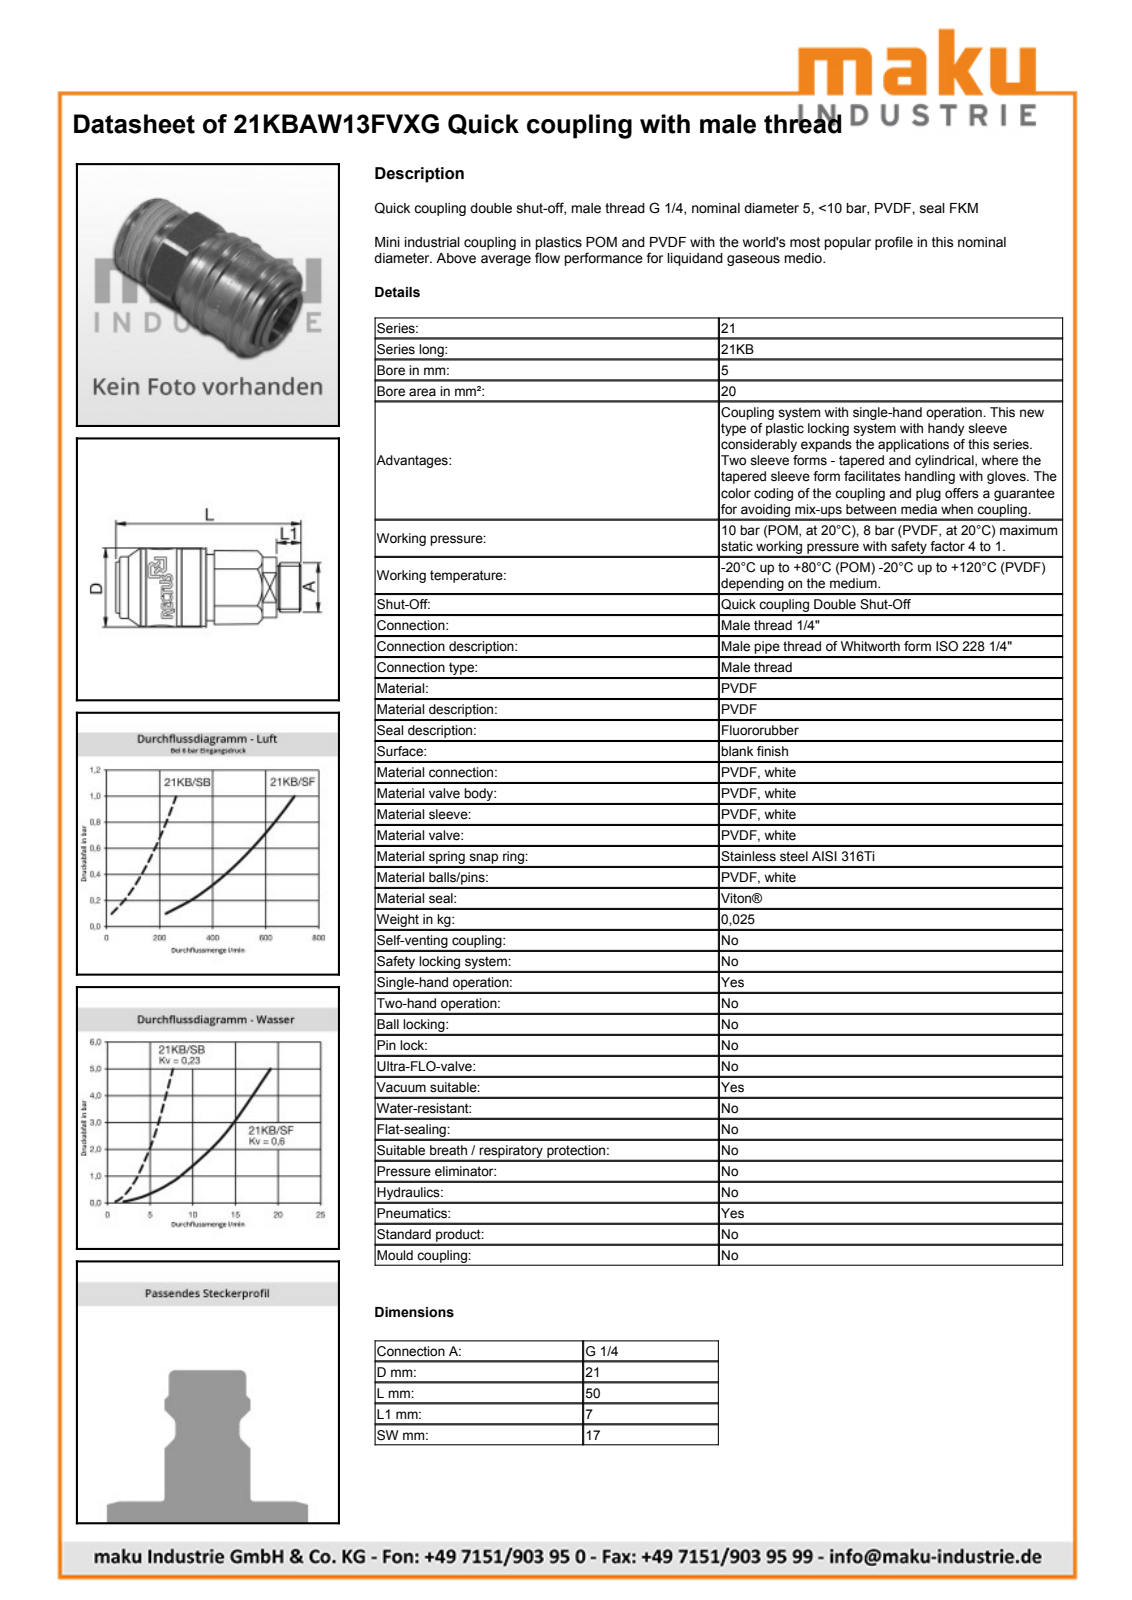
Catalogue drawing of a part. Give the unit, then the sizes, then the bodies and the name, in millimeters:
Units: millimetres
Overall size (bounding box): 49.6 × 21.01 × 21.01
Round holes (diameter × count): ⌀13.15 ×1, ⌀13.6 ×1, ⌀16.7 ×1, ⌀17.8 ×1
Round bosses / shafts (diameter × count): ⌀21 ×1, ⌀20.5 ×1, ⌀17.6 ×1, ⌀16.4 ×1, ⌀14.15 ×1, ⌀13.35 ×1, ⌀13.16 ×1, ⌀13.01 ×1
Partial cylindrical surfaces — rounded edges, fillets, slot ends (radius × count): R8 ×1
Main face-to-face distances: 16.8, 49.6, 25.65, 23.95, 8, 17.65, 41.6, 10.8, 2.8, 14.85
Volume: 10 796 mm³ · Surface area: 6 395 mm²
Bodies: 1 solid, 143 faces (76 planar, 34 cylindrical, 33 other)
Part name (STEP PRODUCT): D108181
STEP written by: Autodesk Inventor 2013 (AUTOMOTIVE_DESIGN)
